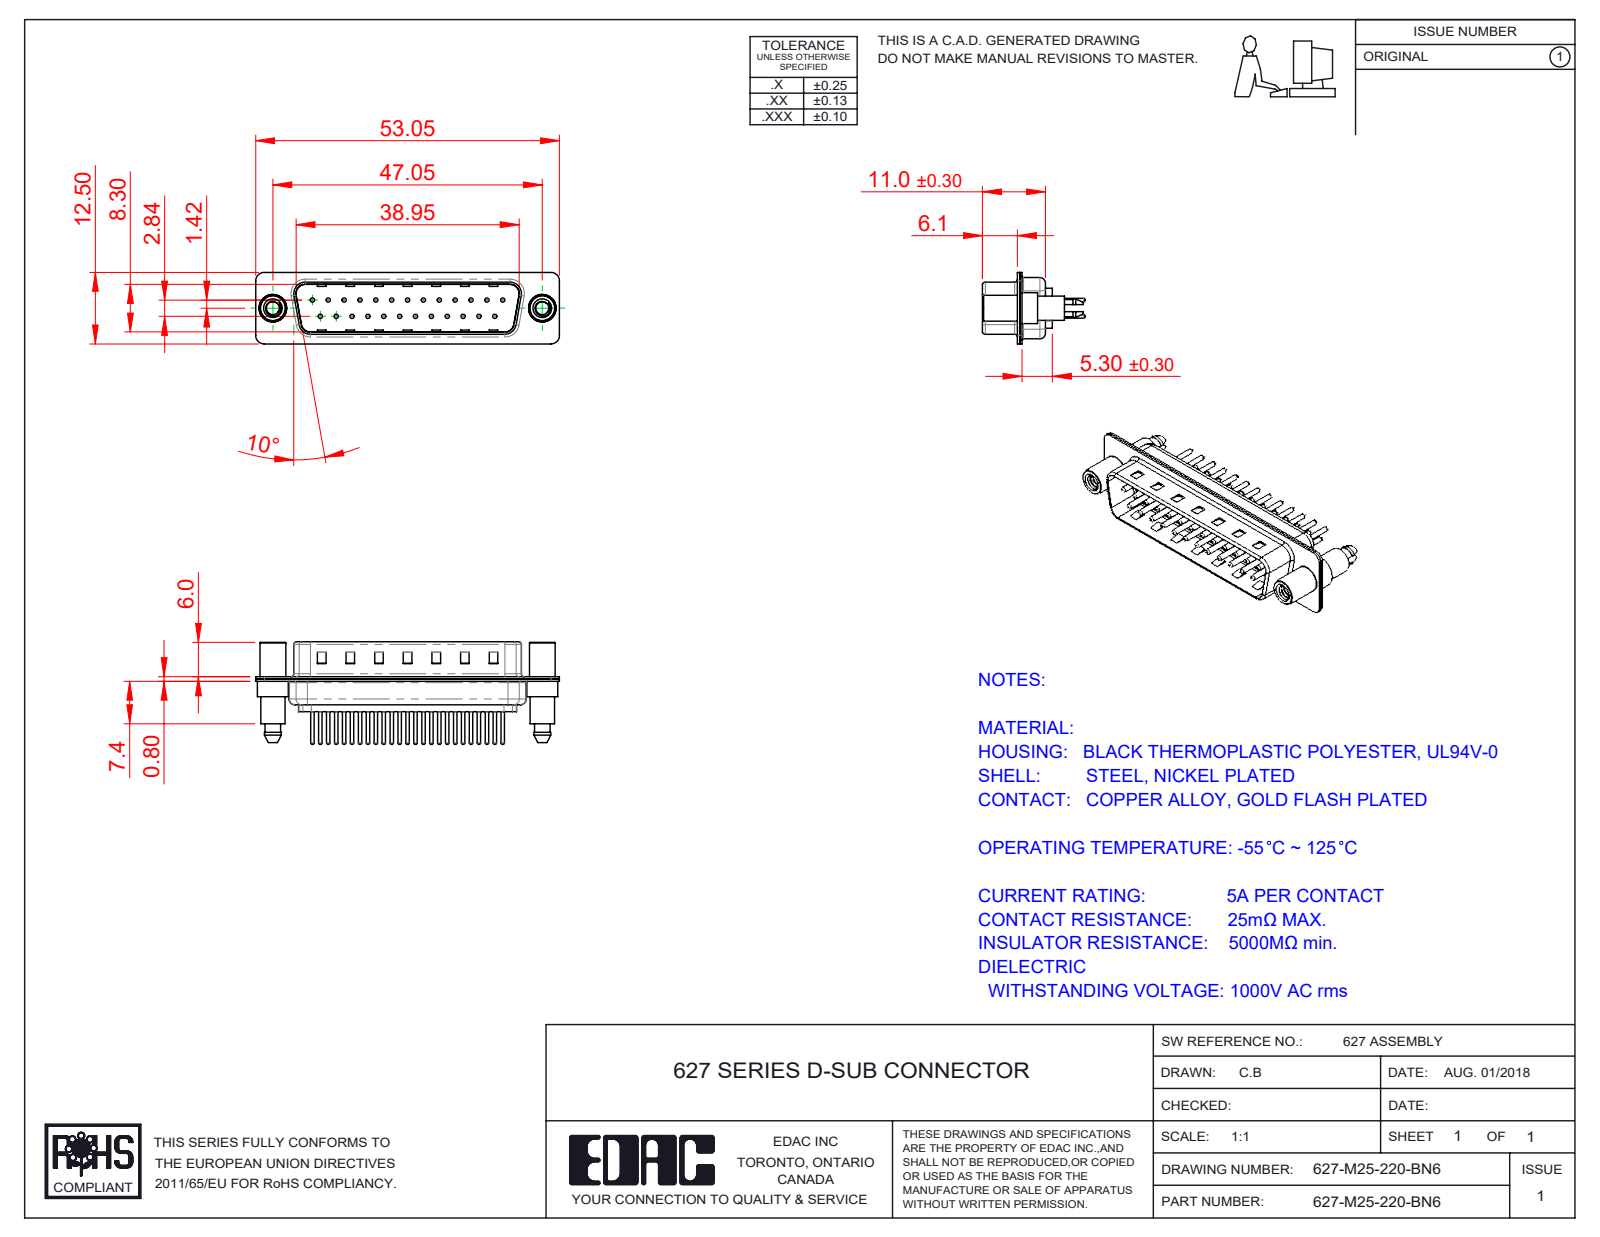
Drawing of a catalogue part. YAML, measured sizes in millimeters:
part_name: "627M Shell Rear_25 Contacts; 627M 4-40 Threaded Standoff and Boardlock; 627M Contact Row 2_20; 627M Contact Row 1_20 (+3 more)"
step_written_by: "SolidWorks 2020 (CONFIG_CONTROL_DESIGN)"
units: millimeters
bodies: {solids: 30, faces: 1353, planar: 364, cylindrical: 515, other: 474}
overall_size: [53.05, 17.9, 12.5]
volume: 3058
surface_area: 7311
round_holes:
  - {diameter: 0.75, count: 25}
  - {diameter: 1.6, count: 25}
  - {diameter: 2, count: 25}
  - {diameter: 2.26, count: 2}
  - {diameter: 4, count: 2}
  - {diameter: 4.8, count: 2}
round_bosses_or_shafts:
  - {diameter: 1.5, count: 25}
  - {diameter: 0.6, count: 25}
  - {diameter: 5.4, count: 2}
  - {diameter: 4.9, count: 2}
  - {diameter: 4.5, count: 2}
  - {diameter: 4.25, count: 2}
partial_cylinders:
  - {radius: 1.5, count: 18}
  - {radius: 2, count: 12}
  - {radius: 1.6, count: 10}
  - {radius: 0.5, count: 8}
  - {radius: 0.25, count: 4}
  - {radius: 0.6, count: 4}
  - {radius: 0.65, count: 4}
  - {radius: 0.9, count: 4}
face_to_face_distances: [0.4, 0.8, 9.5, 9.1, 8.7, 9.9, 1.2, 5.7, 6.1, 0.75]
hole_center_spacings: [3.16, 2.77, 5.54, 8.31, 11.08, 13.85, 16.62, 5.03]
